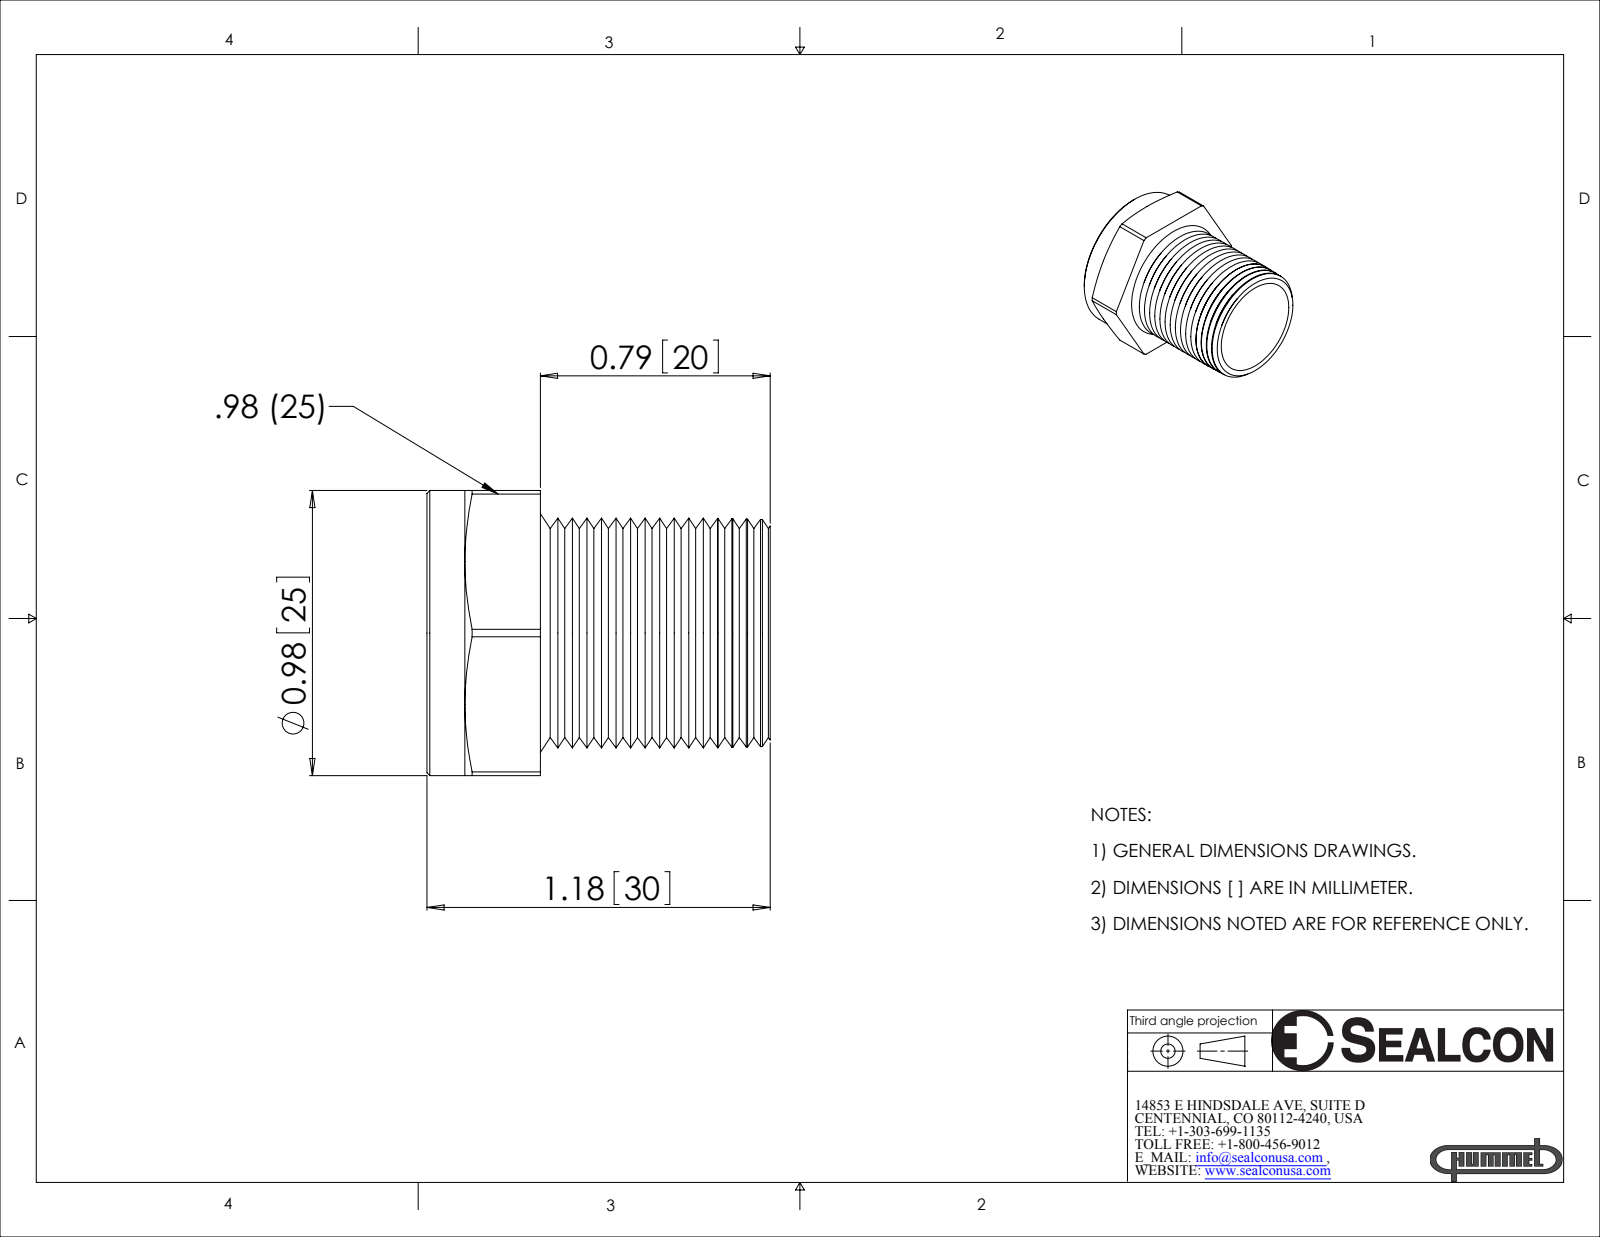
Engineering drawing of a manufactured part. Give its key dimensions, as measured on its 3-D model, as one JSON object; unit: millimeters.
{"part_name": "AT-1216-BR", "step_written_by": "SolidWorks 2008 (CONFIG_CONTROL_DESIGN)", "units": "millimeters", "bodies": {"solids": 1, "faces": 131, "planar": 11, "cylindrical": 13, "other": 107}, "overall_size": [30, 28.4, 24.9], "volume_mm3": 4600, "surface_area_mm2": 5239, "round_holes": [[16.6, 1], [16.7, 1]], "round_bosses_or_shafts": [[24.9, 1]], "partial_cylinders_radius": [[14.2, 1]], "face_to_face_distances": [24.9, 9.9, 20.1, 30, 24.6, 4.5, 5.4, 21.6, 1.5, 3]}
